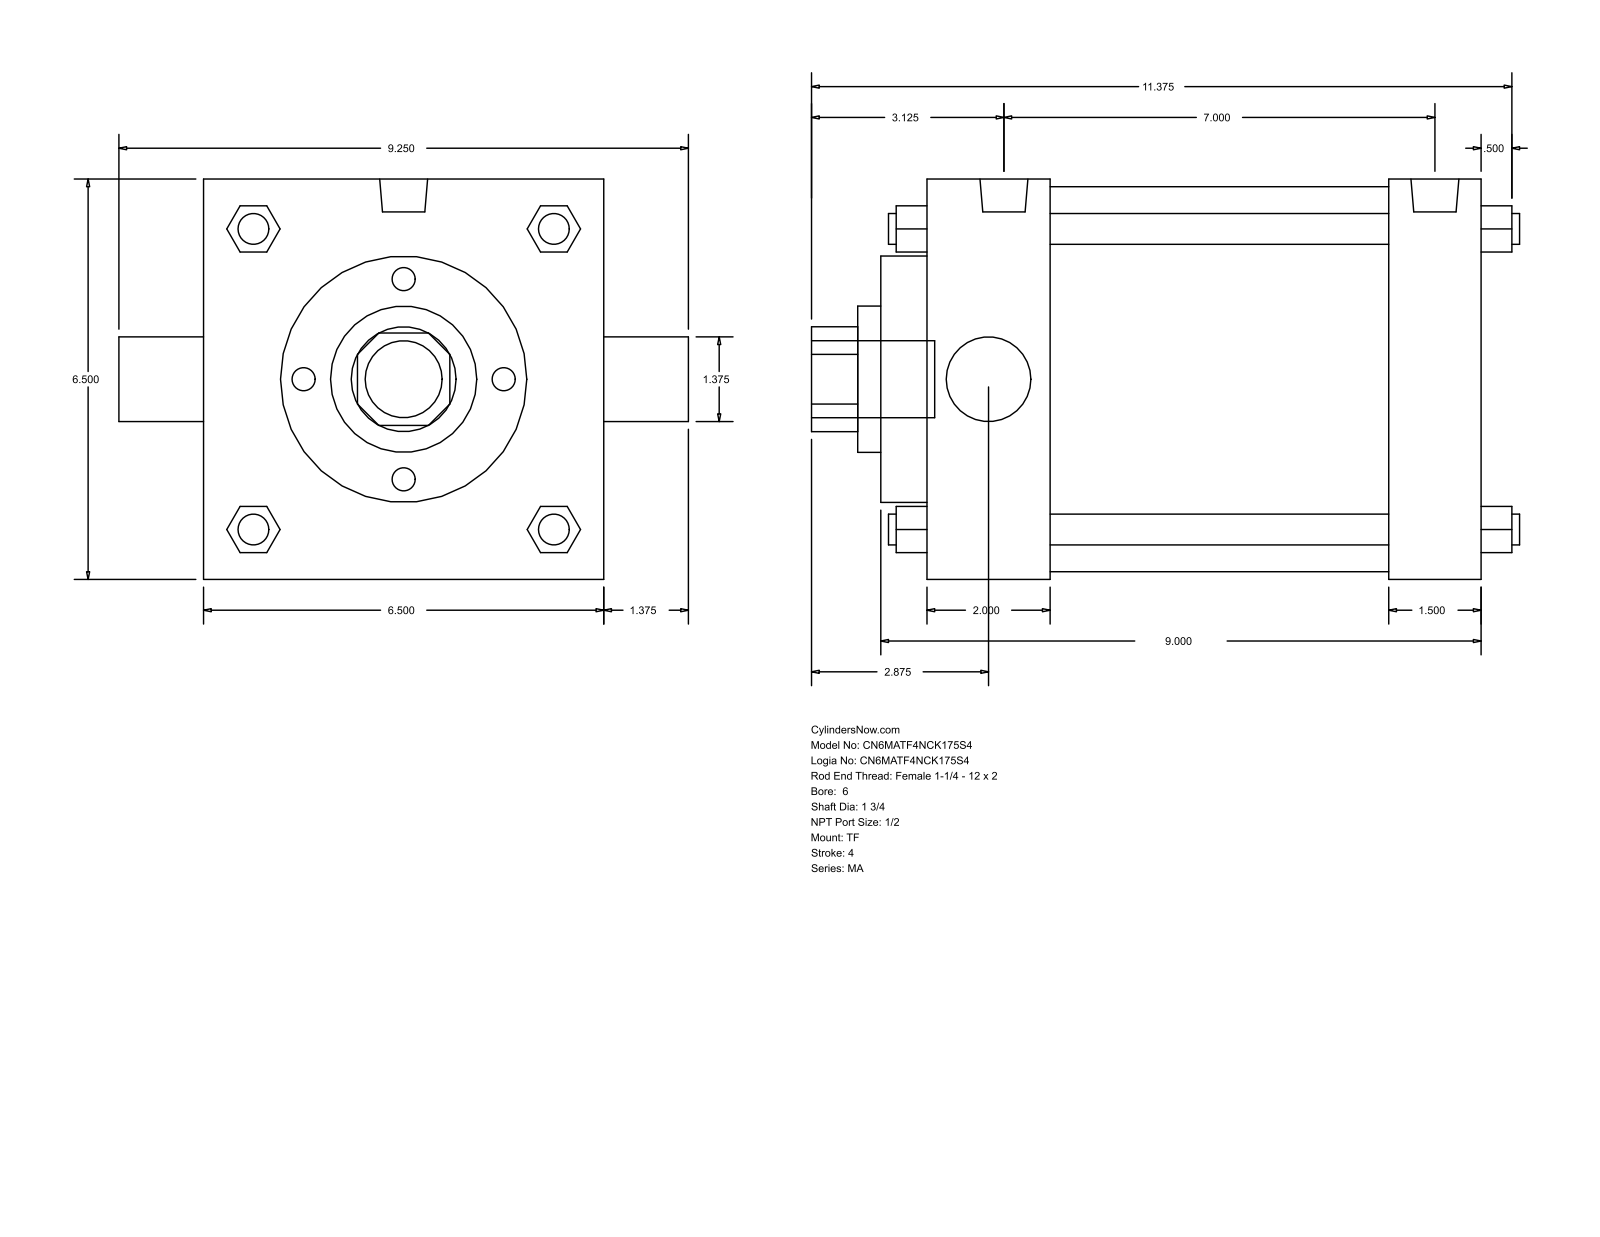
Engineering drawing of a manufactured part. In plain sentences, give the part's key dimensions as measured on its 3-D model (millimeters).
The part is named "MA_TF__0600_1.75". Its 3-D file was written by "GSSL Pune (CONFIG_CONTROL_DESIGN)". It is 0 solids with 122 faces: 93 planar, 29 cylindrical and 0 other. Overall it measures 292.1 by 234.95 by 165.1 millimeters. Round holes: 1 of diameter 34.92, 1 of diameter 44.45, 1 of diameter 60.33, 1 of diameter 101.6, 1 of diameter 158.75. Round bosses or shafts: 4 of diameter 12.7, 3 of diameter 17.46, 2 of diameter 19.77, 1 of diameter 31.75. Partial cylindrical surfaces (rounded edges, fillets, slot ends): 1 of radius 21.63. The main face-to-face distances are 165.1, 228.61, 19.05, 50.8, 177.81, 190.5, 139.7, 38.11, 69.85, 209.55.
